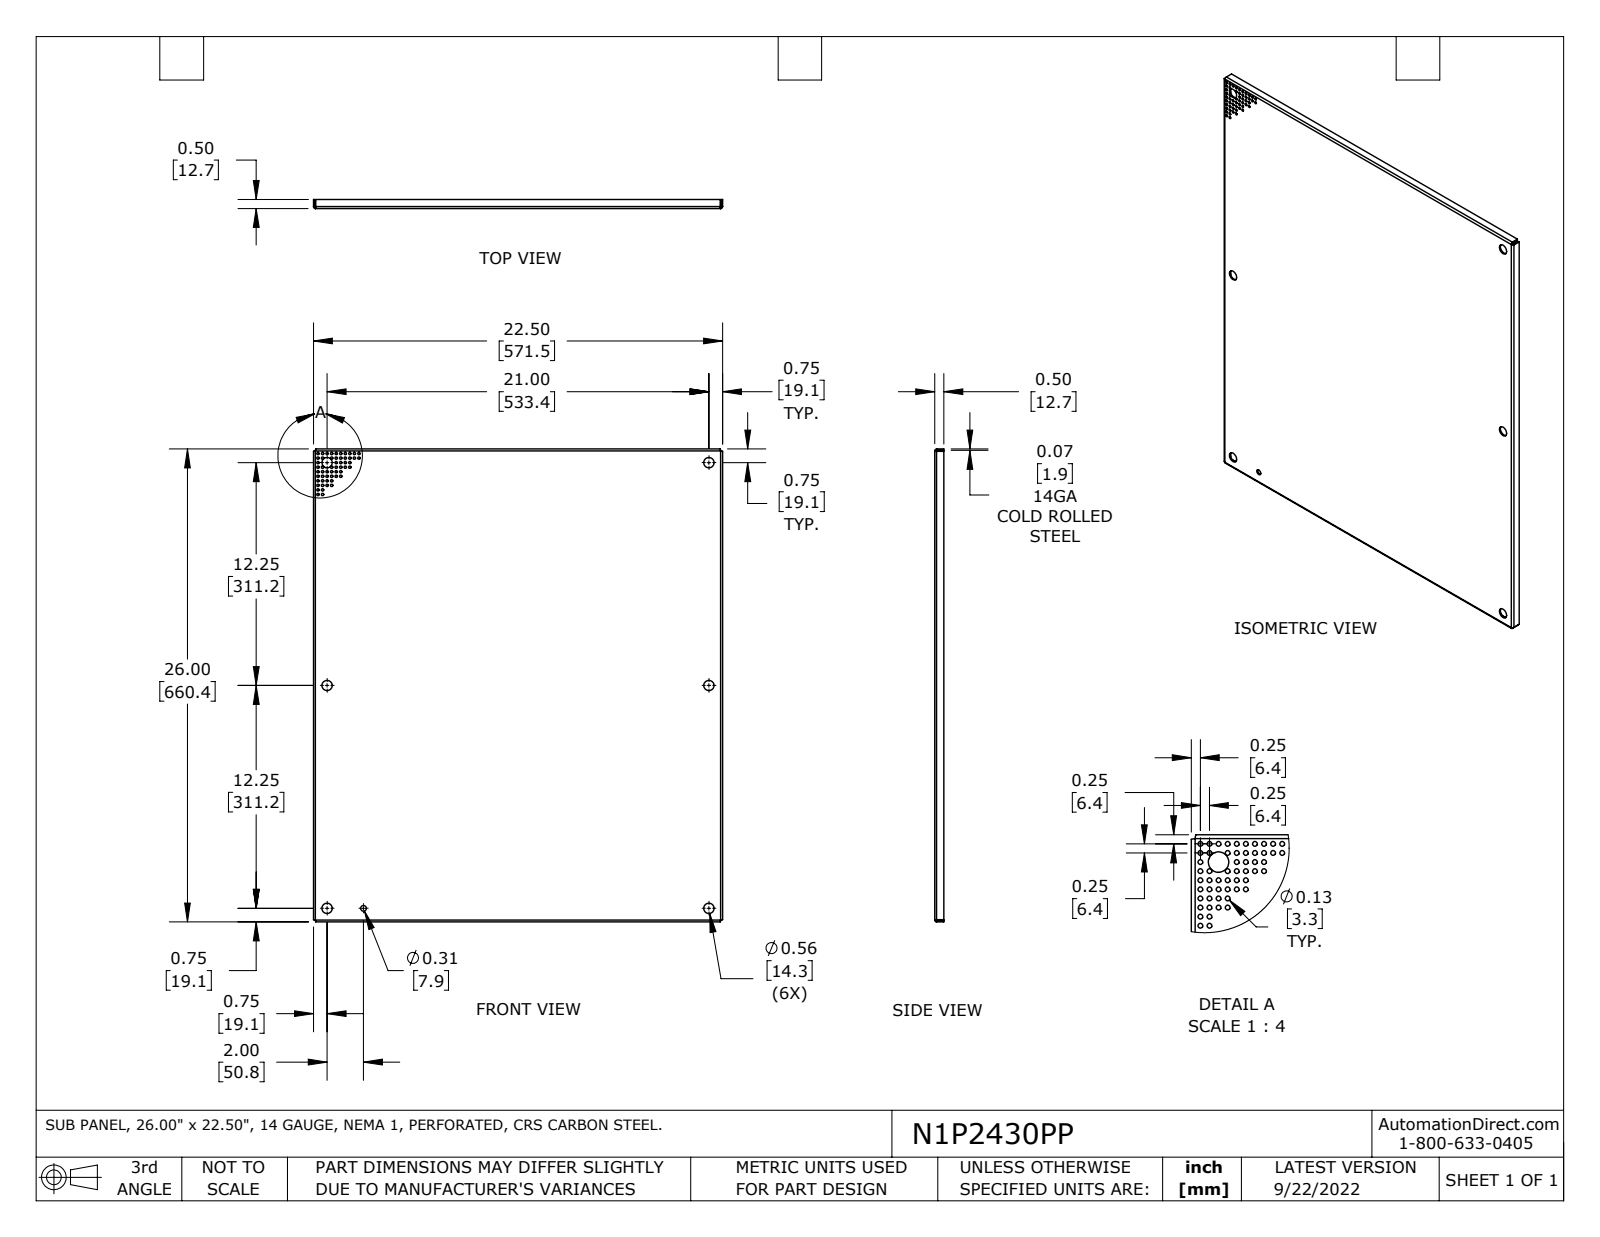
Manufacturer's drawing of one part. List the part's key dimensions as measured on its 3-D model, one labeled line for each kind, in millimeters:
Part name (STEP PRODUCT): N1P2430PP
STEP written by: SolidWorks 2021 (AUTOMOTIVE_DESIGN)
Units: millimetres
Bodies: 1 solid, 162 faces (22 planar, 132 cylindrical, 8 other)
Overall size (bounding box): 660.4 × 571.5 × 12.7
Volume: 752 700 mm³ · Surface area: 807 100 mm²
Round holes (diameter × count): ⌀3.3 ×55, ⌀14.3 ×6, ⌀7.9 ×1
Partial cylindrical surfaces — rounded edges, fillets, slot ends (radius × count): R0.8 ×4, R2.7 ×4
Main face-to-face distances: 1.9, 569.6, 658.5, 571.5, 567.7, 656.6, 660.4, 10.8, 12.7, 3.2
Hole centre spacings: 6.4, 14.2, 31.8, 20.1, 12.7, 26.2, 9, 22.9
